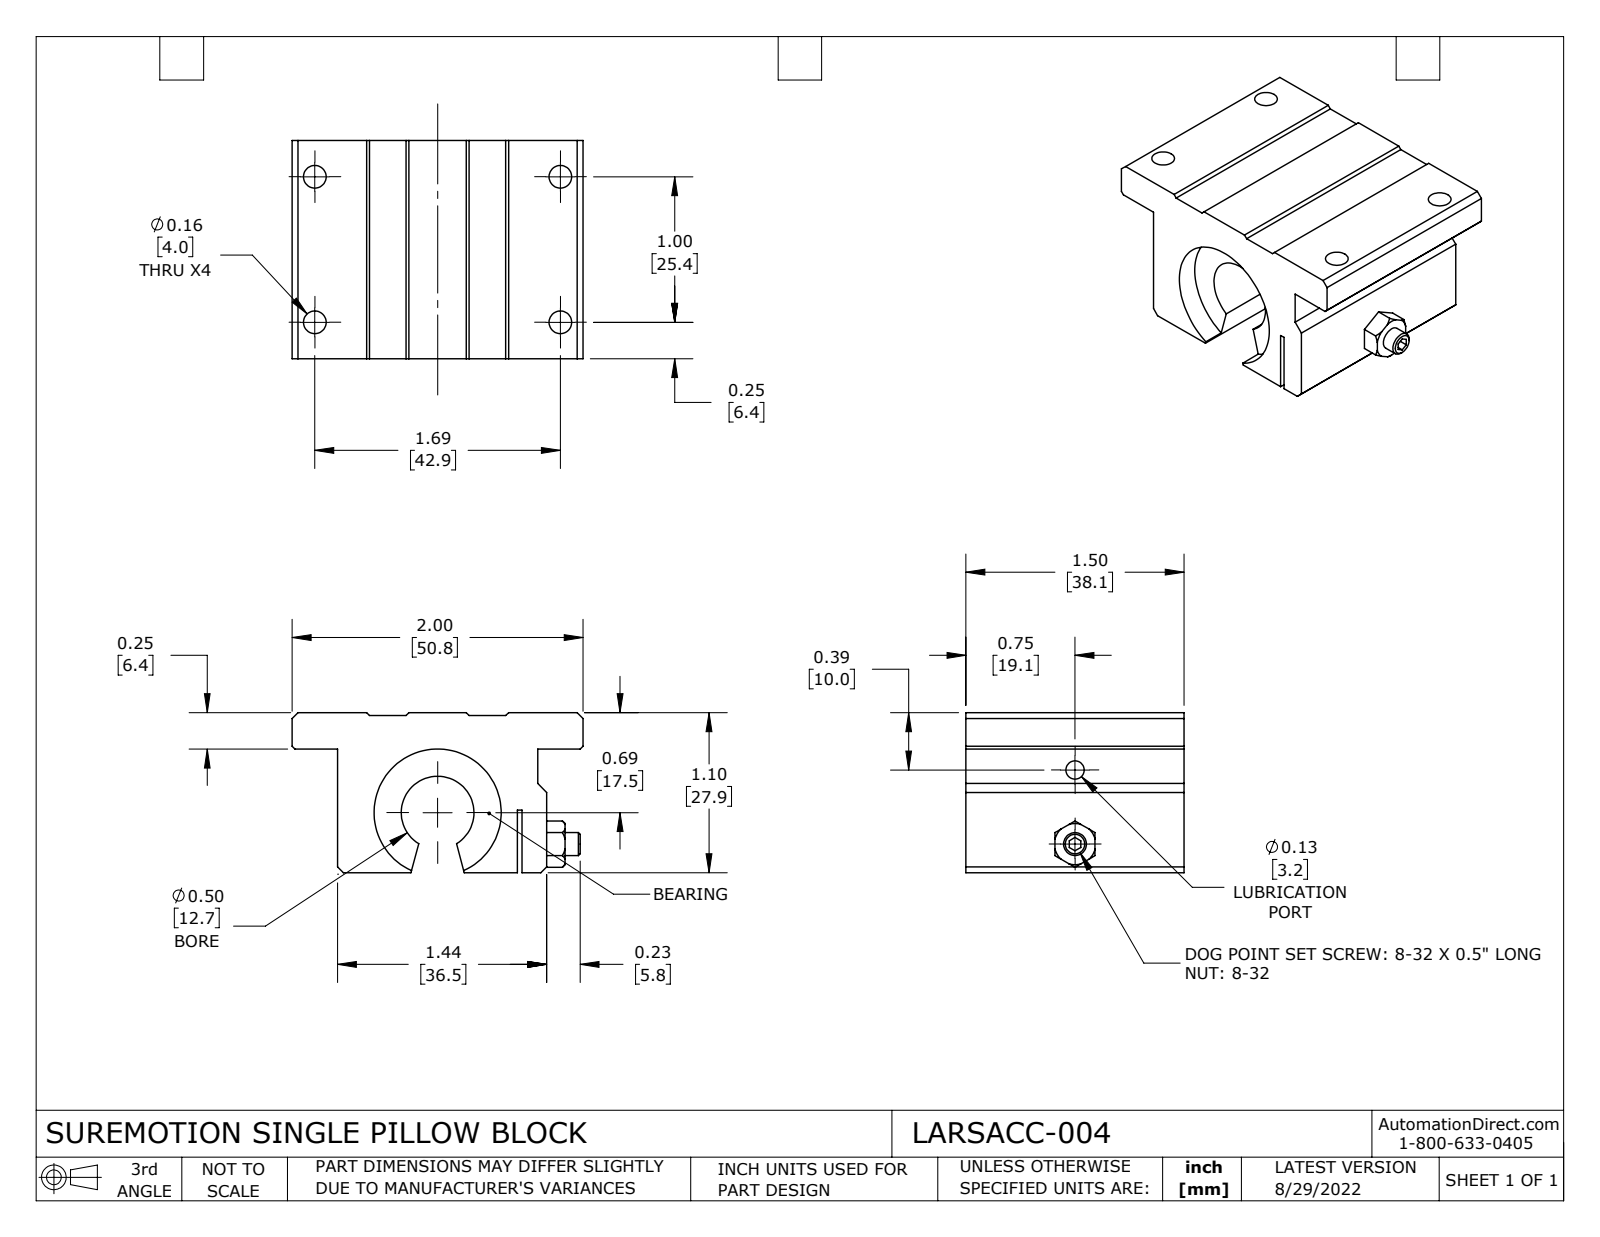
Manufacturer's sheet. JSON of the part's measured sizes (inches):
{"part_name": "LARSACC-004", "step_written_by": "SolidWorks 2021 (CONFIG_CONTROL_DESIGN)", "units": "inches", "bodies": {"solids": 1, "faces": 81, "planar": 51, "cylindrical": 22, "other": 8}, "overall_size": [2, 1.5, 1.1], "volume_in3": 2.021, "surface_area_in2": 16.34, "round_holes": [[0.156, 4], [0.126, 1], [0.5, 1], [0.874, 1]], "round_bosses_or_shafts": [[0.157, 1]], "face_to_face_distances": [1.1, 0.25, 1.5, 0.85, 1.08, 0.23, 0.02, 1.438, 0.15, 1.35], "hole_center_spacings": [1, 1.688, 1.962]}
